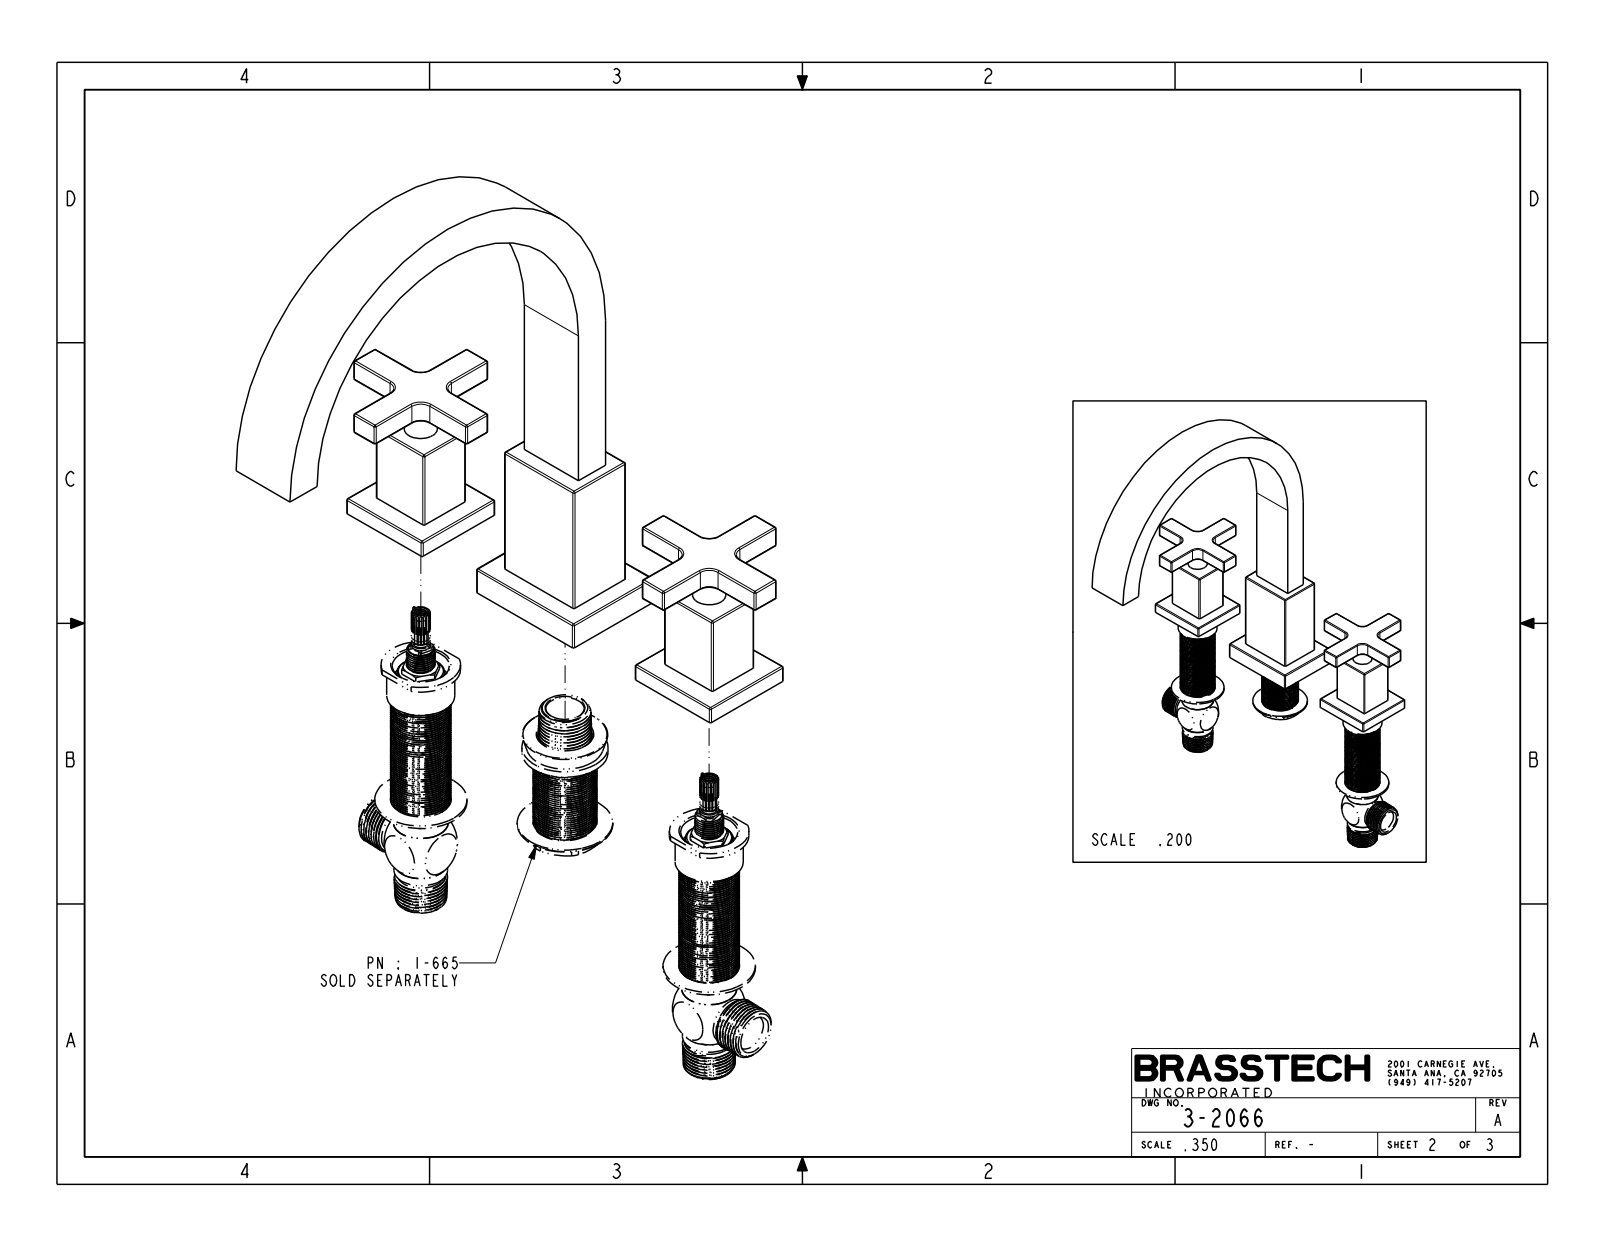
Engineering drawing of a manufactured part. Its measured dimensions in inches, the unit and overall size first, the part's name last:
Units: inches
Overall size (bounding box): 11.224 × 11.14 × 9.945
Round bosses / shafts (diameter × count): ⌀0.65 ×2, ⌀0.523 ×2
Partial cylindrical surfaces — rounded edges, fillets, slot ends (radius × count): R0.03 ×84, R0.25 ×8, R3.625 ×1, R4.375 ×1
Main face-to-face distances: 1.5, 0.345, 1.095, 1.72, 0.14, 1.3, 0.205, 0.955, 0.22, 8
Volume: 40.91 in³ · Surface area: 172.8 in²
Bodies: 3 solids, 274 faces (68 planar, 130 cylindrical, 76 other)
Part name (STEP PRODUCT): 3-2066
STEP written by: CREO PARAMETRIC BY PTC INC, 2018400 (CONFIG_CONTROL_DESIGN)
